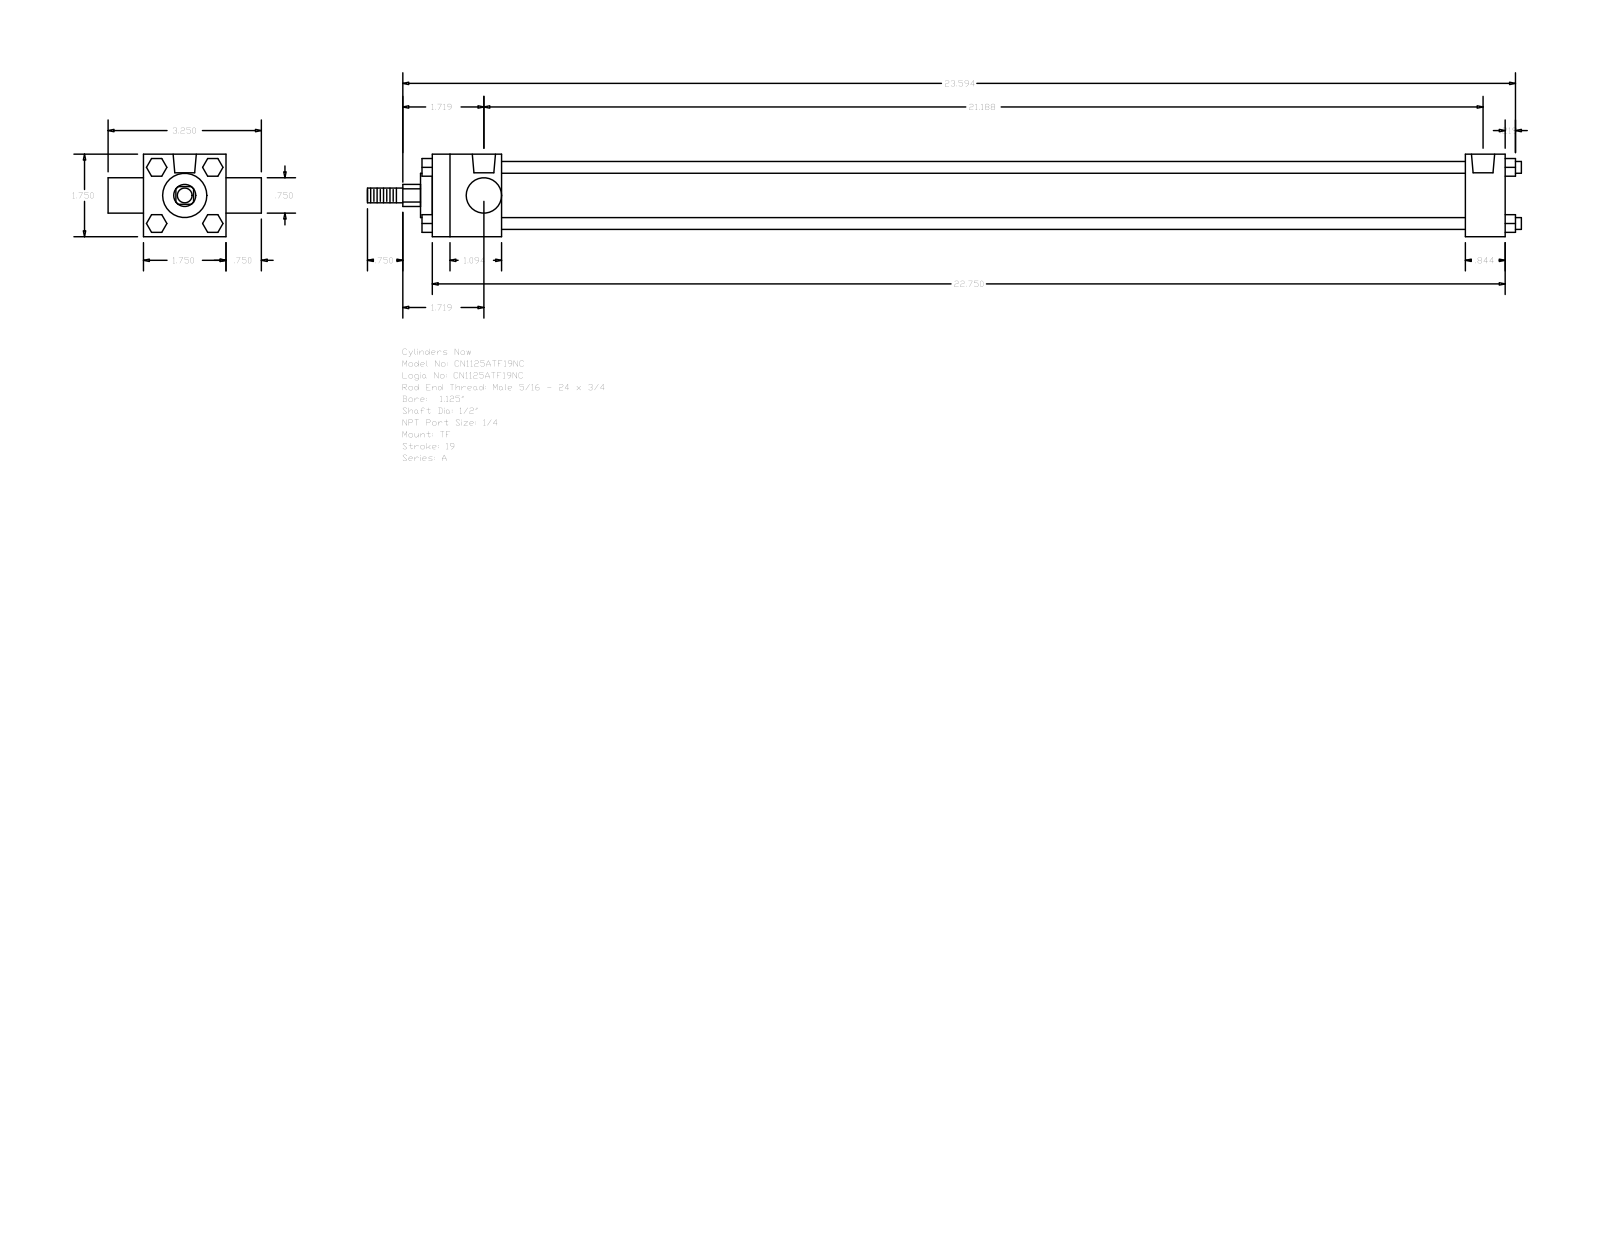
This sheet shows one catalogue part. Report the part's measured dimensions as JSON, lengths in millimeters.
{"part_name": "A_TF__0112_0.5", "step_written_by": "GSSL Pune (CONFIG_CONTROL_DESIGN)", "units": "millimeters", "bodies": {"solids": 0, "faces": 120, "planar": 92, "cylindrical": 28, "other": 0}, "overall_size": [621.51, 82.55, 44.45], "round_holes": [[5.56, 3], [12.49, 2]], "round_bosses_or_shafts": [[6.35, 4], [31.88, 1], [23.81, 1], [19.05, 1], [12.7, 1], [7.94, 1]], "partial_cylinders_radius": [[5.94, 1]], "face_to_face_distances": [44.46, 577.85, 556.41, 21.44, 37.3, 519.11, 540.55, 19.04, 63.5, 9.53], "hole_center_spacings": [1.58, 1.59, 534.99, 536.57, 536.58, 538.16]}
